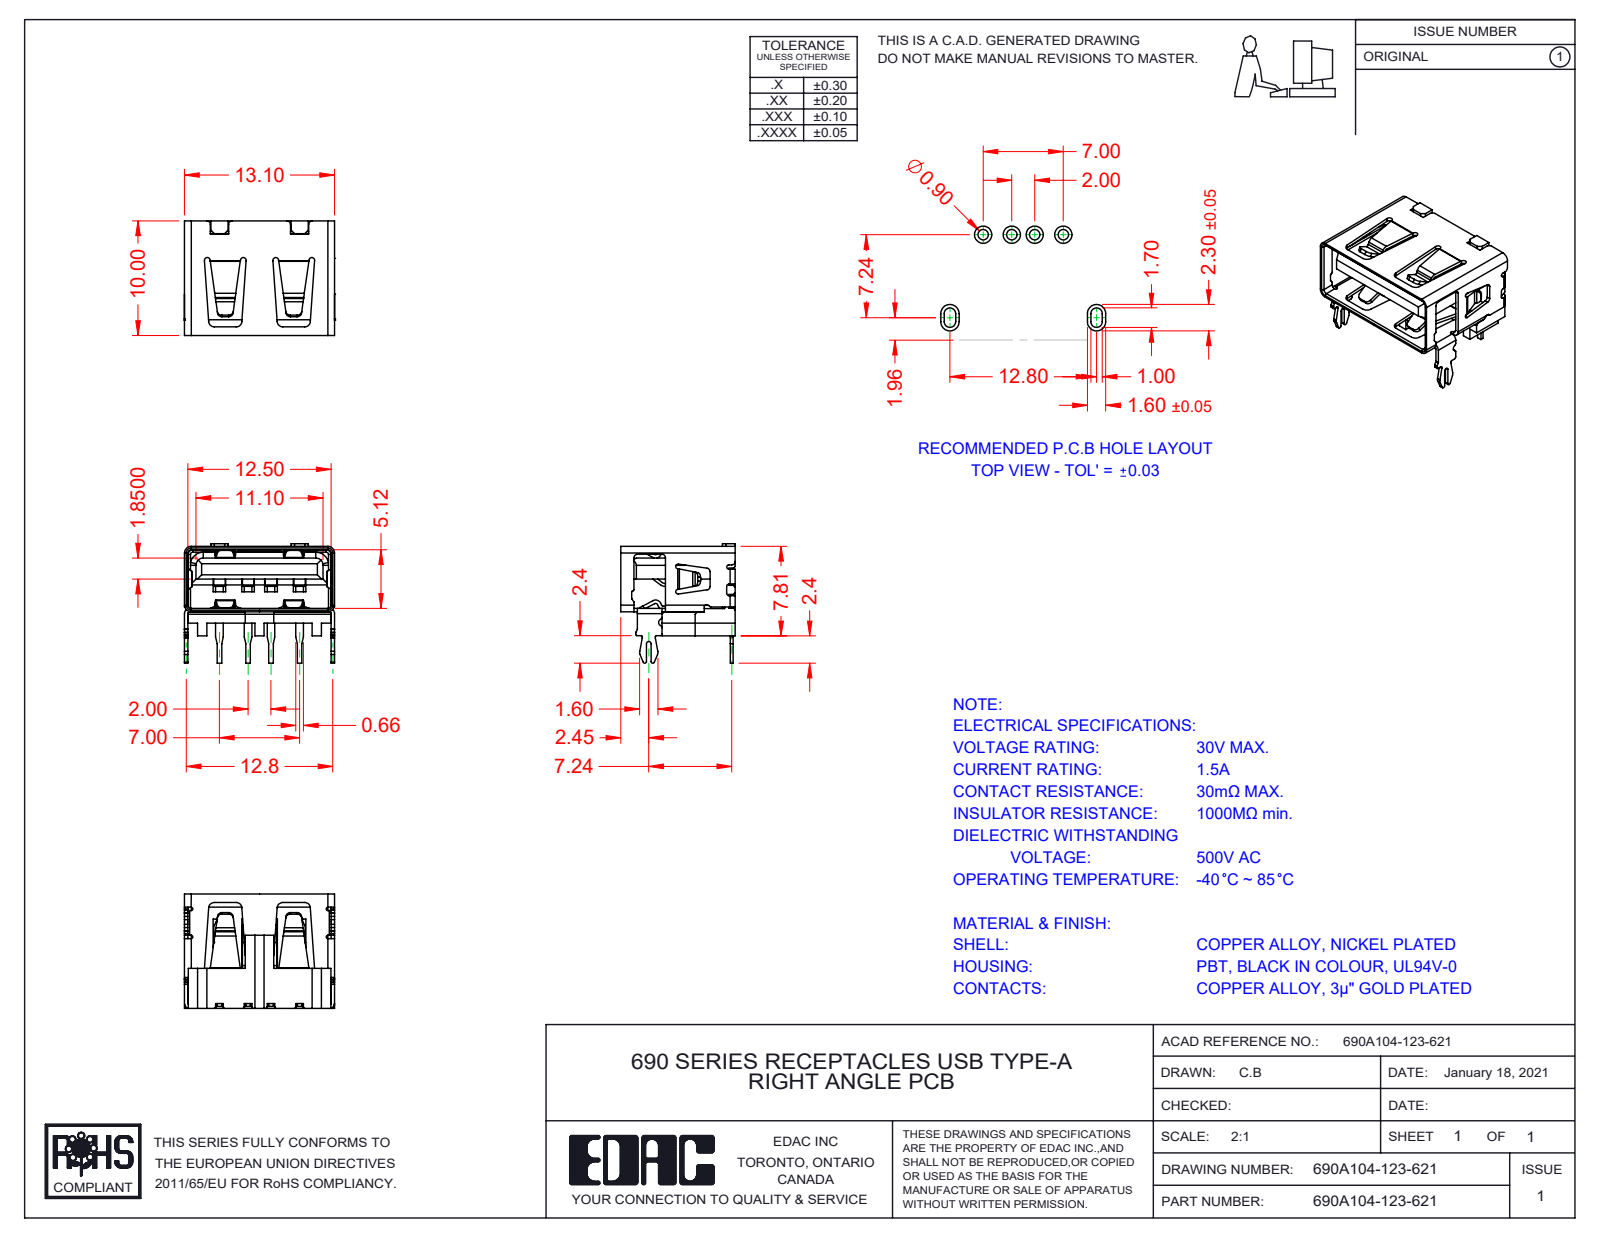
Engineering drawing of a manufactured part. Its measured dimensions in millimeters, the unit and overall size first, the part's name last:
Units: millimetres
Overall size (bounding box): 13.1 × 10.43 × 10
Partial cylindrical surfaces — rounded edges, fillets, slot ends (radius × count): R0.1 ×22, R0.2 ×18, R0.3 ×18, R0.4 ×15, R0.5 ×14, R0.15 ×13, R0.45 ×6, R0.59 ×6
Main face-to-face distances: 5.42, 1.4, 4.7, 0.72, 2.5, 1.02, 0.45, 2.55, 12.8, 1.1
Volume: 327 mm³ · Surface area: 1 425 mm²
Bodies: 6 solids, 949 faces (599 planar, 232 cylindrical, 118 other)
Part name (STEP PRODUCT): 690A104-123-621; Shell 690A104-123-621; Insulator 690A104-123-621; Contact 690A104-123-621
STEP written by: SolidWorks 2020 (AUTOMOTIVE_DESIGN)
